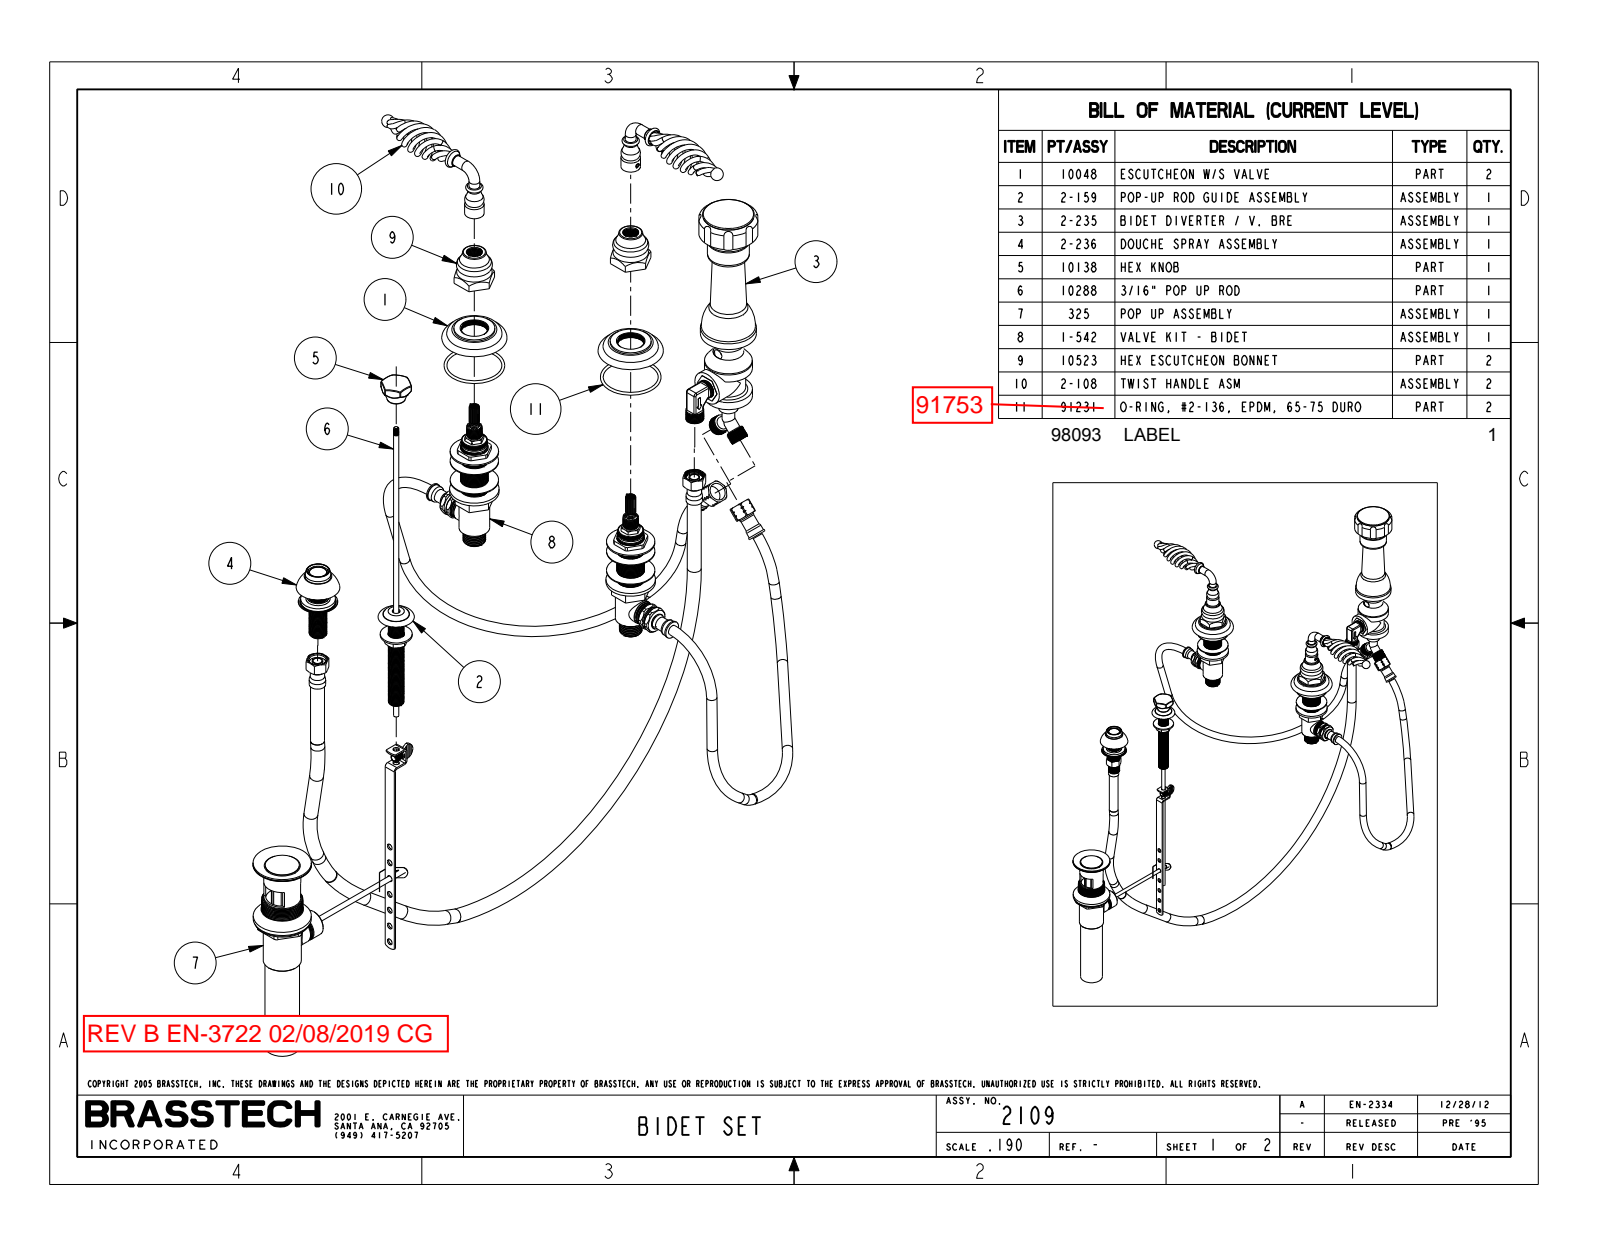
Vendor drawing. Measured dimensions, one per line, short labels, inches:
name: 2109_WEB
written by: PRO/ENGINEER BY PARAMETRIC TECHNOLOGY CORPORATION, 2009300 (CONFIG_CONTROL_DESIGN)
unit: in
bodies: 0 solids, 291 faces (43 planar, 48 cylindrical, 200 other)
size: 22.855 × 17.289 × 5.372
bosses: 3× ⌀0.39, 2× ⌀1.482, 2× ⌀0.705, 2× ⌀0.475, 1× ⌀2.025, 1× ⌀1.52, 1× ⌀0.926
rounds: 8× R0.21, 6× R0.03, 1× R1.077
face distances: 0.375, 0.437, 0.062, 0.019, 0.356, 0.418, 3.487, 3.468, 3.112, 3.05
